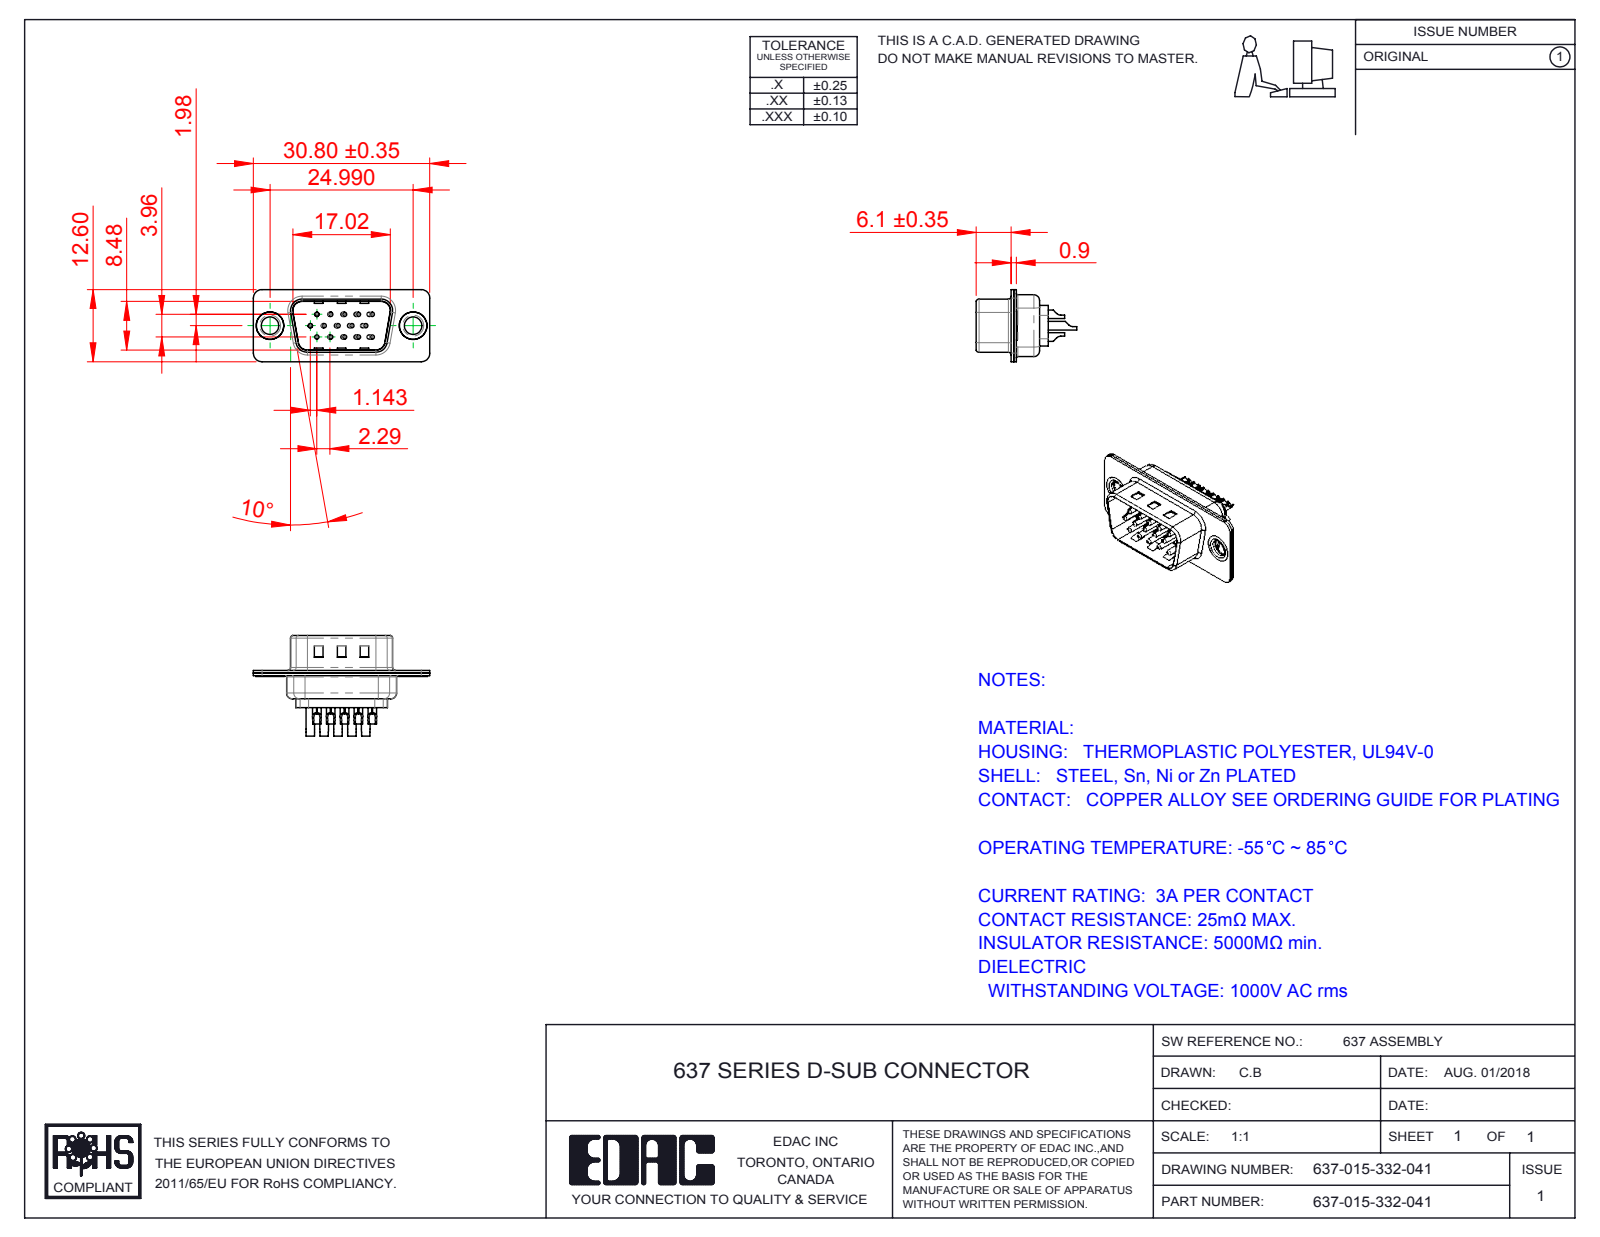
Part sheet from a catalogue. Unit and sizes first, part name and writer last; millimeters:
Units: millimetres
Overall size (bounding box): 30.8 × 17.55 × 12.6
Round holes (diameter × count): ⌀1.6 ×27, ⌀0.35 ×15, ⌀1.1 ×15, ⌀0.75 ×12, ⌀2 ×12, ⌀3.05 ×2, ⌀4 ×2, ⌀4.8 ×2
Round bosses / shafts (diameter × count): ⌀2 ×15, ⌀1.5 ×15, ⌀0.75 ×15, ⌀5 ×2, ⌀4.9 ×2, ⌀3.55 ×2
Partial cylindrical surfaces — rounded edges, fillets, slot ends (radius × count): R1.5 ×16, R2 ×12, R0.5 ×8, R1 ×7, R0.25 ×4, R0.55 ×4, R0.7 ×4, R0.95 ×4
Main face-to-face distances: 0.45, 0.9, 0.4, 0.7, 8.48, 8.88, 1.05, 0.31, 4.55, 1.16
Hole centre spacings: 3.96, 2.29, 2.28, 4.57, 2.42, 6.05, 4.84, 2.35
Volume: 1 253 mm³ · Surface area: 4 633 mm²
Bodies: 20 solids, 1238 faces (317 planar, 548 cylindrical, 373 other)
Part name (STEP PRODUCT): 637 Contact Row 1_32; 637 Shell Rear_15 Contacts; 637-015-332-041; 637 Shell Front_15 Contacts (+4 more)
STEP written by: SolidWorks 2016 (CONFIG_CONTROL_DESIGN)
